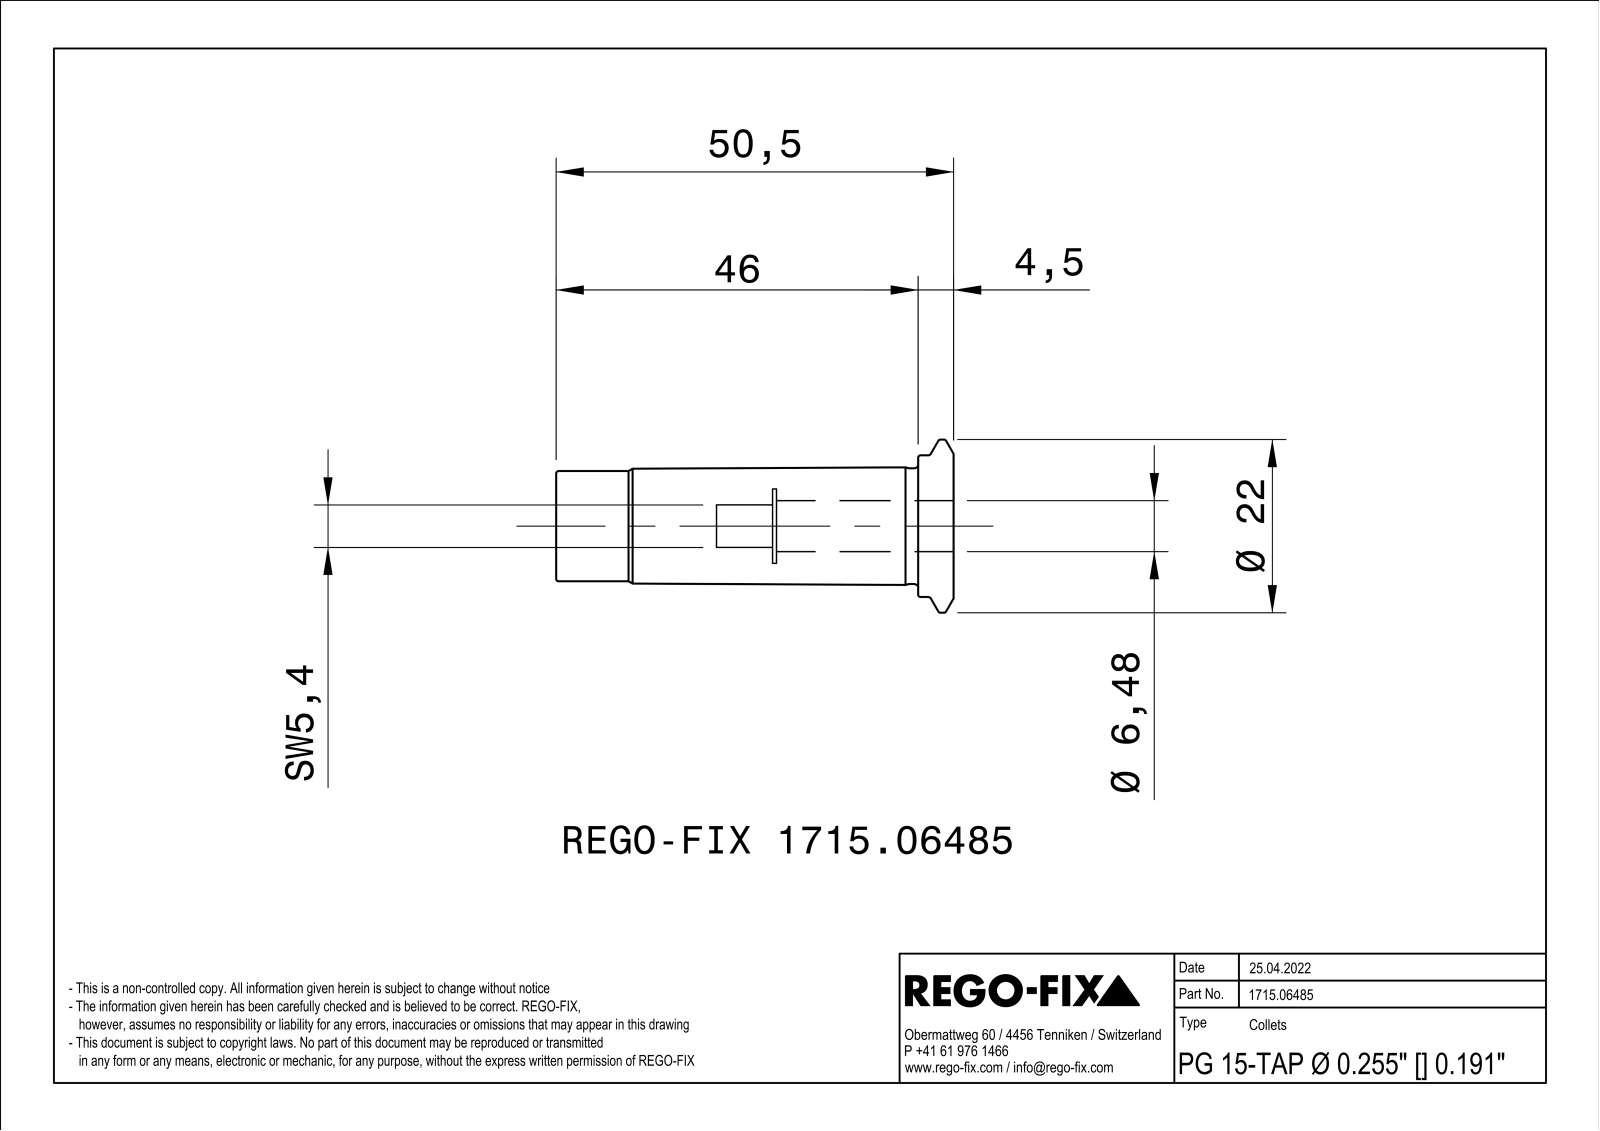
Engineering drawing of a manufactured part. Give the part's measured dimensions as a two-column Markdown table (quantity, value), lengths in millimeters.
| quantity | value |
| --- | --- |
| part name | NOCUT |
| STEP written by | SIEMENS PLM Software Solid Edge ST10 (AUTOMOTIVE_DESIGN) |
| units | millimeters |
| bodies | 1 solid, 104 faces (25 planar, 28 cylindrical, 51 other) |
| overall size | 50.5 × 22 × 21.99 |
| volume | 6 617 mm³ |
| surface area | 6 030 mm² |
| round holes (diameter × count) | 6.48 × 1, 6.92 × 1, 7 × 1, 8.4 × 1, 11.1 × 1 |
| round bosses / shafts (diameter × count) | 22 × 1, 18 × 1, 14.7 × 1, 14 × 1, 11 × 1, 10.9 × 1, 10.5 × 1, 10.2 × 1 |
| main face-to-face distances | 1, 50.5, 5.1, 21, 29.5, 7, 22.5, 28, 4.5, 23 |
